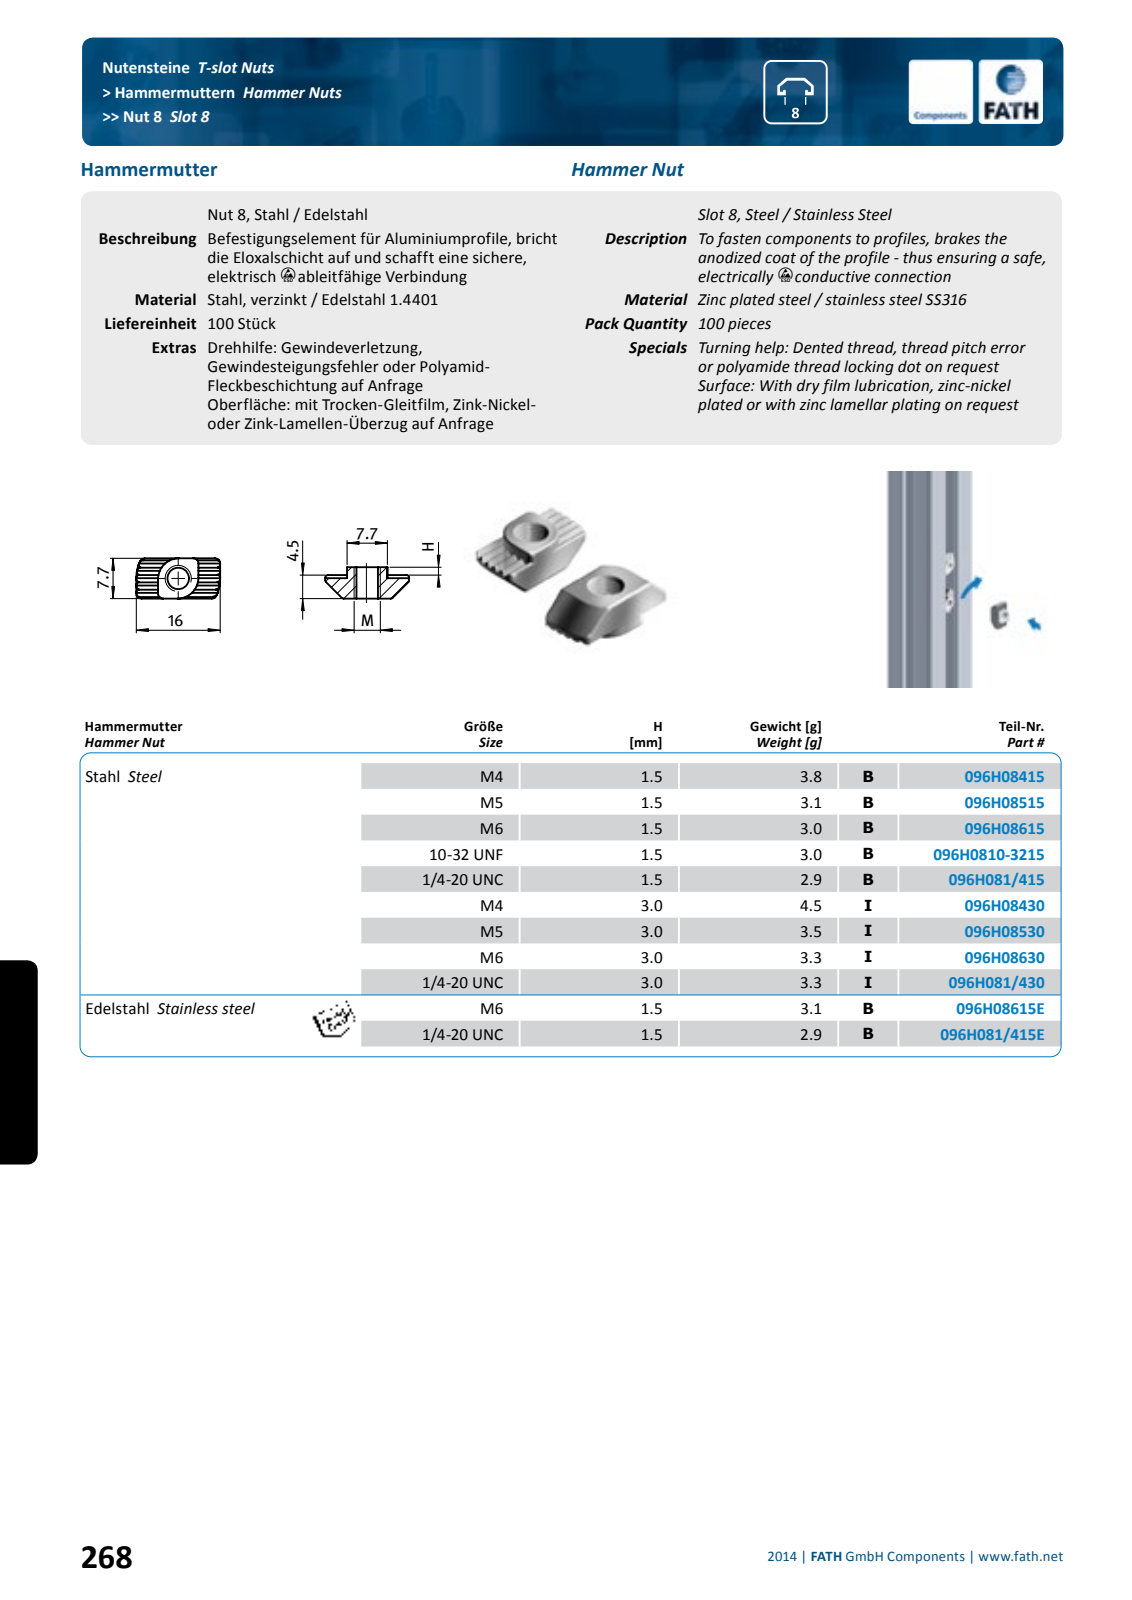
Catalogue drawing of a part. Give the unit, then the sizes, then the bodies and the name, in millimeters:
Units: millimetres
Overall size (bounding box): 16.5 × 8 × 6
Round holes (diameter × count): ⌀5 ×1
Partial cylindrical surfaces — rounded edges, fillets, slot ends (radius × count): R0.3 ×14, R0.1 ×9, R0.5 ×6, R3.95 ×2, R8.25 ×1
Main face-to-face distances: 8, 0.71, 2.12, 1.41, 2.83, 6, 4.24, 3.53, 1.42, 0.7
Volume: 480 mm³ · Surface area: 548 mm²
Bodies: 1 solid, 122 faces (42 planar, 50 cylindrical, 30 other)
Part name (STEP PRODUCT): fath_096h08615e
STEP written by: Spatial InterOp 3D (automotive_design)
